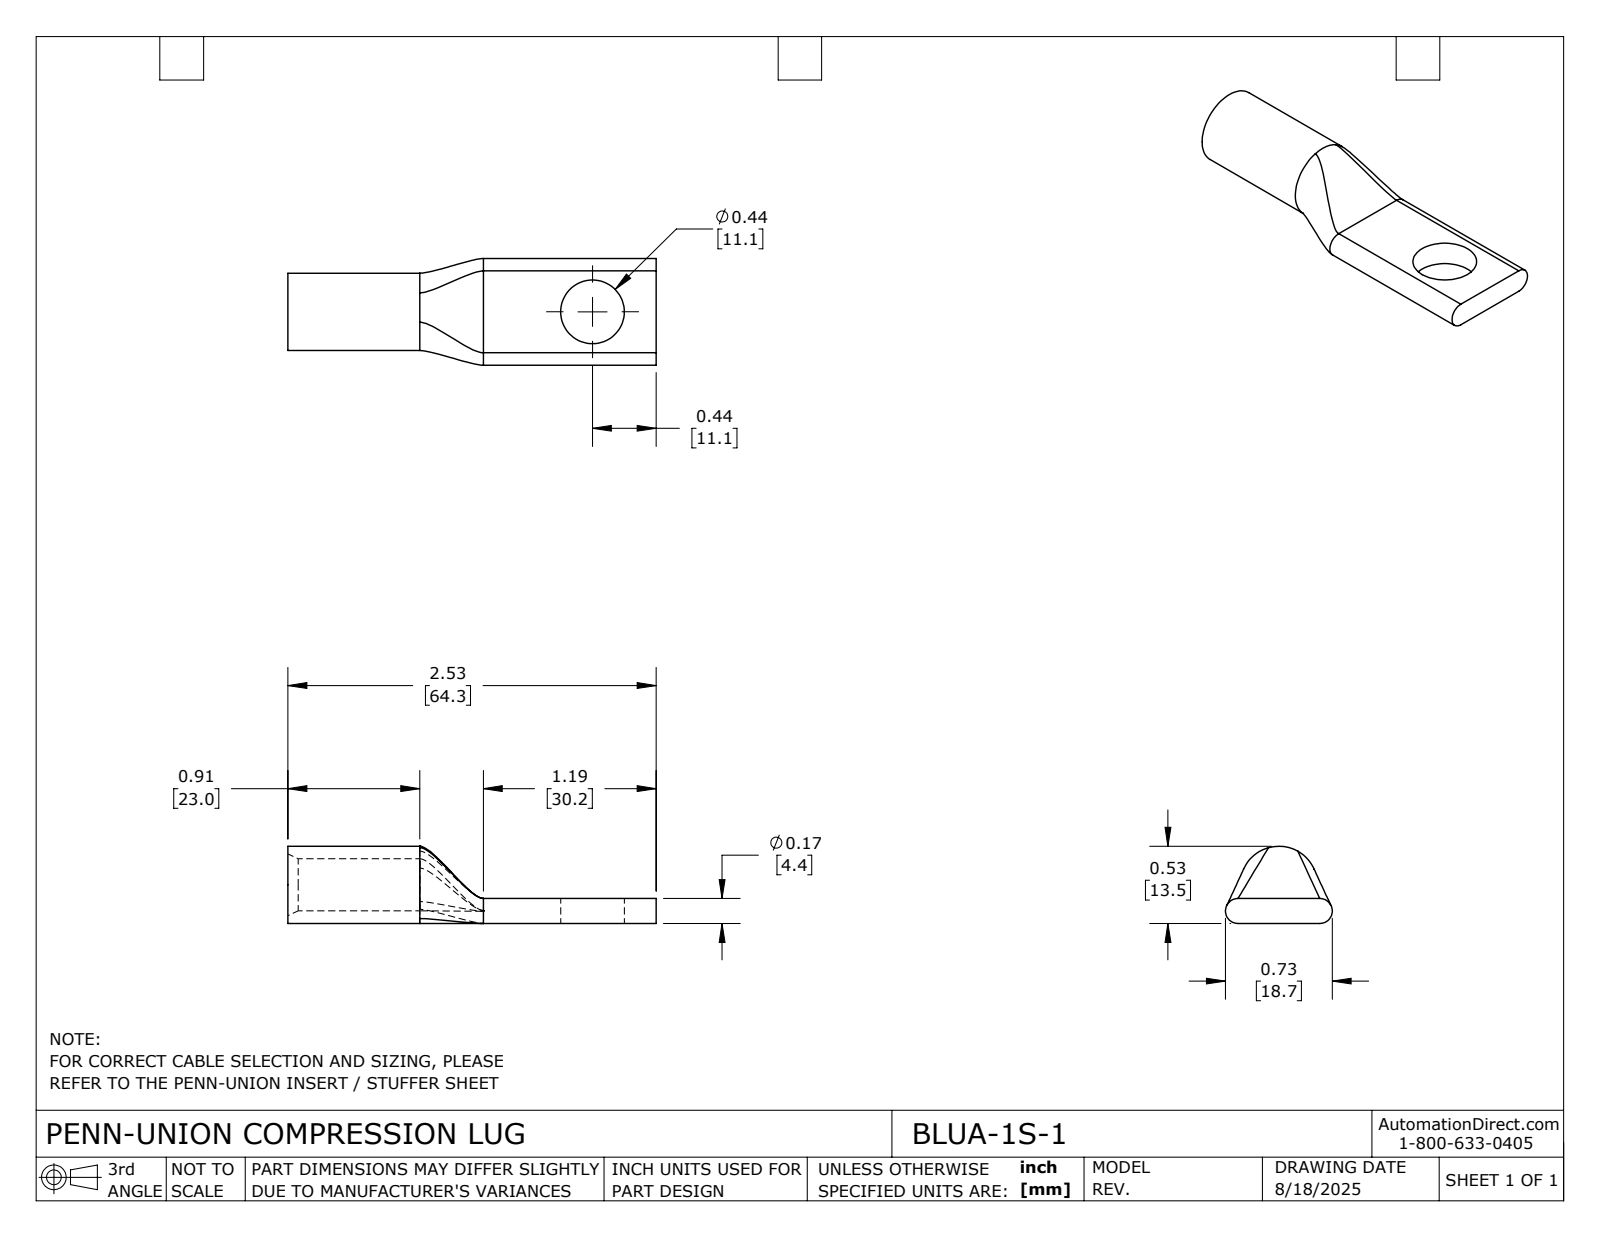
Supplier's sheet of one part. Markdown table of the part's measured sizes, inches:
| quantity | value |
| --- | --- |
| part name | BLUA-1S-1 |
| STEP written by | SolidWorks 2024 (CONFIG_CONTROL_DESIGN) |
| units | inches |
| bodies | 1 solid, 24 faces (5 planar, 9 cylindrical, 10 other) |
| overall size | 2.531 × 0.734 × 0.531 |
| volume | 0.277 in³ |
| surface area | 5.994 in² |
| round holes (diameter × count) | 0.358 × 1, 0.437 × 1 |
| round bosses / shafts (diameter × count) | 0.531 × 1 |
| partial cylindrical surfaces (radius × count) | 0.086 × 2 |
| main face-to-face distances | 0.172, 2.531, 1.344, 1.187 |
